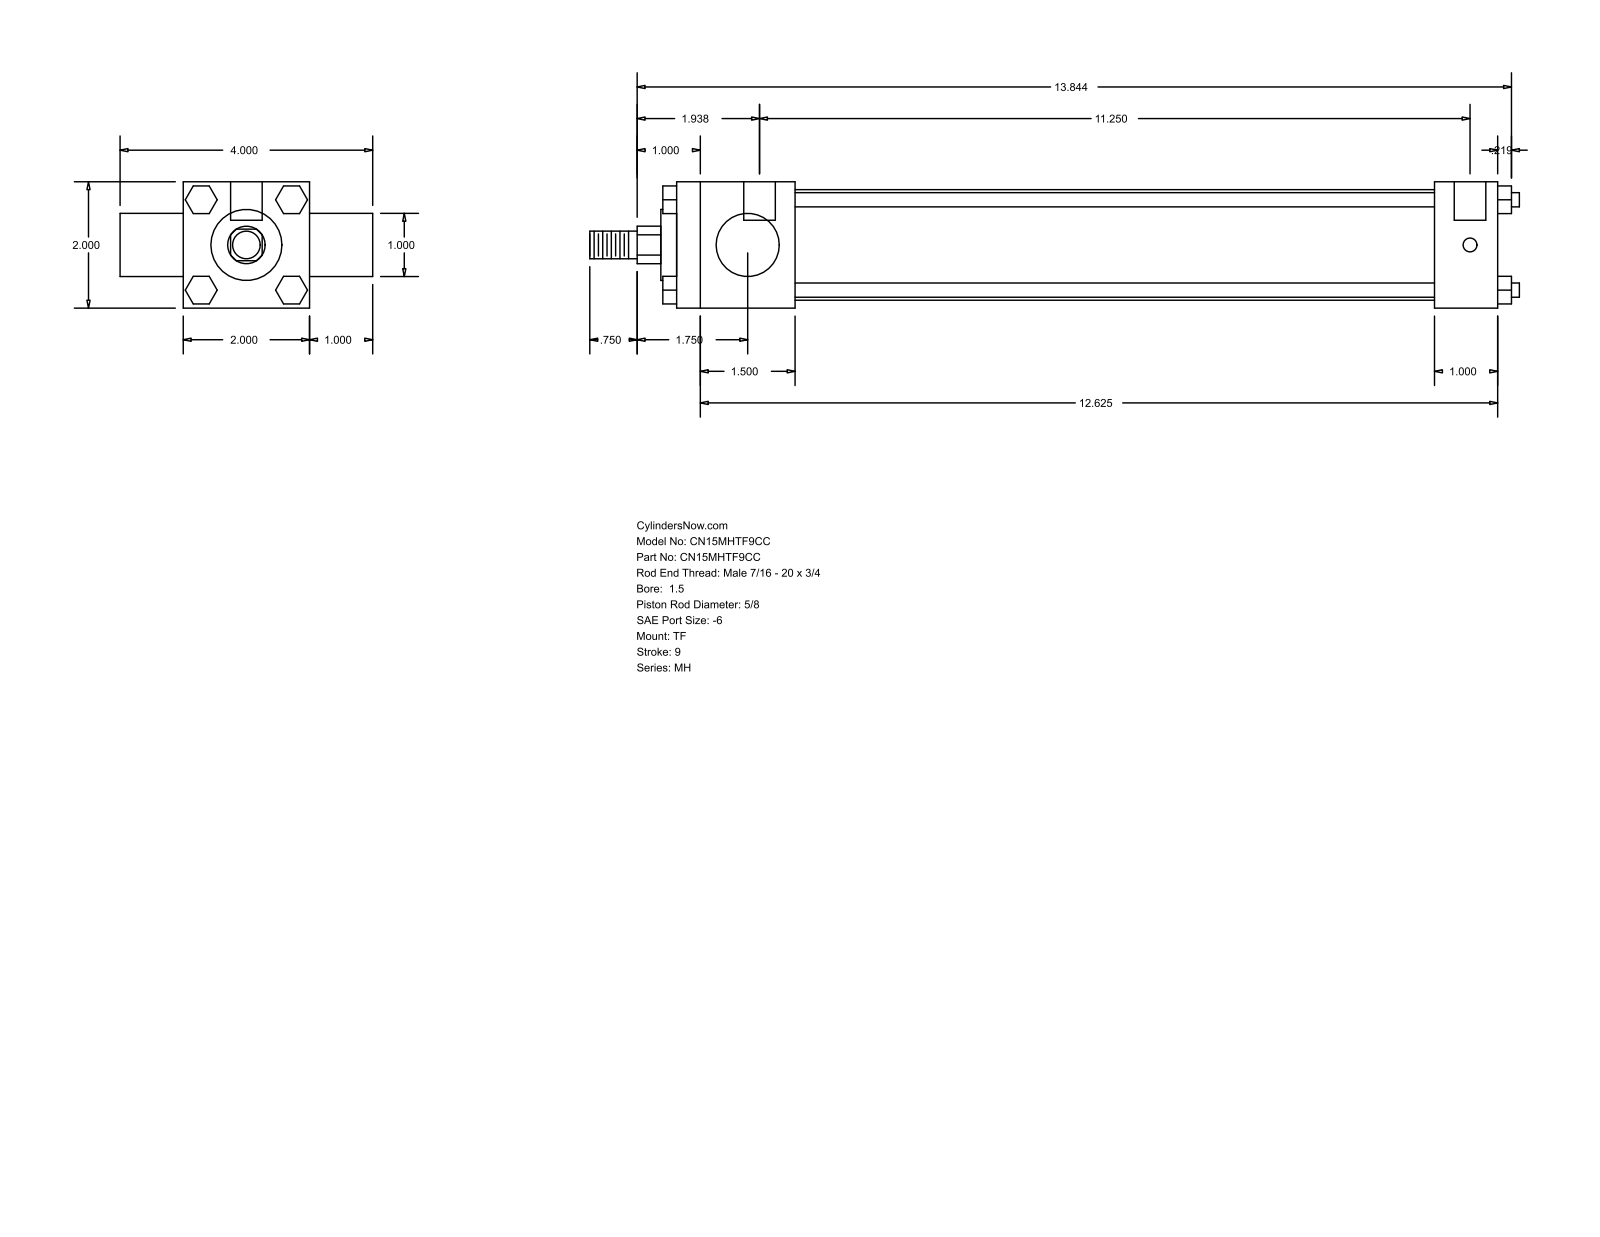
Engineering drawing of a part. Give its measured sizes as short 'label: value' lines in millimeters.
name: MH_TF__0150_0.625
written by: GSSL Pune (CONFIG_CONTROL_DESIGN)
unit: mm
bodies: 0 solids, 120 faces (92 planar, 28 cylindrical, 0 other)
size: 373.86 × 101.6 × 50.8
holes: 3× ⌀5.56, 2× ⌀12.7
bosses: 4× ⌀5.71, 1× ⌀44.45, 1× ⌀28.57, 1× ⌀25.4, 1× ⌀15.88, 1× ⌀11.11
rounds: 1× R7.54
face distances: 50.8, 330.19, 25.4, 76.2, 47.62, 282.57, 304.8, 257.18, 25.39, 5.56
hole spacings: 3.17, 285.75, 288.92
